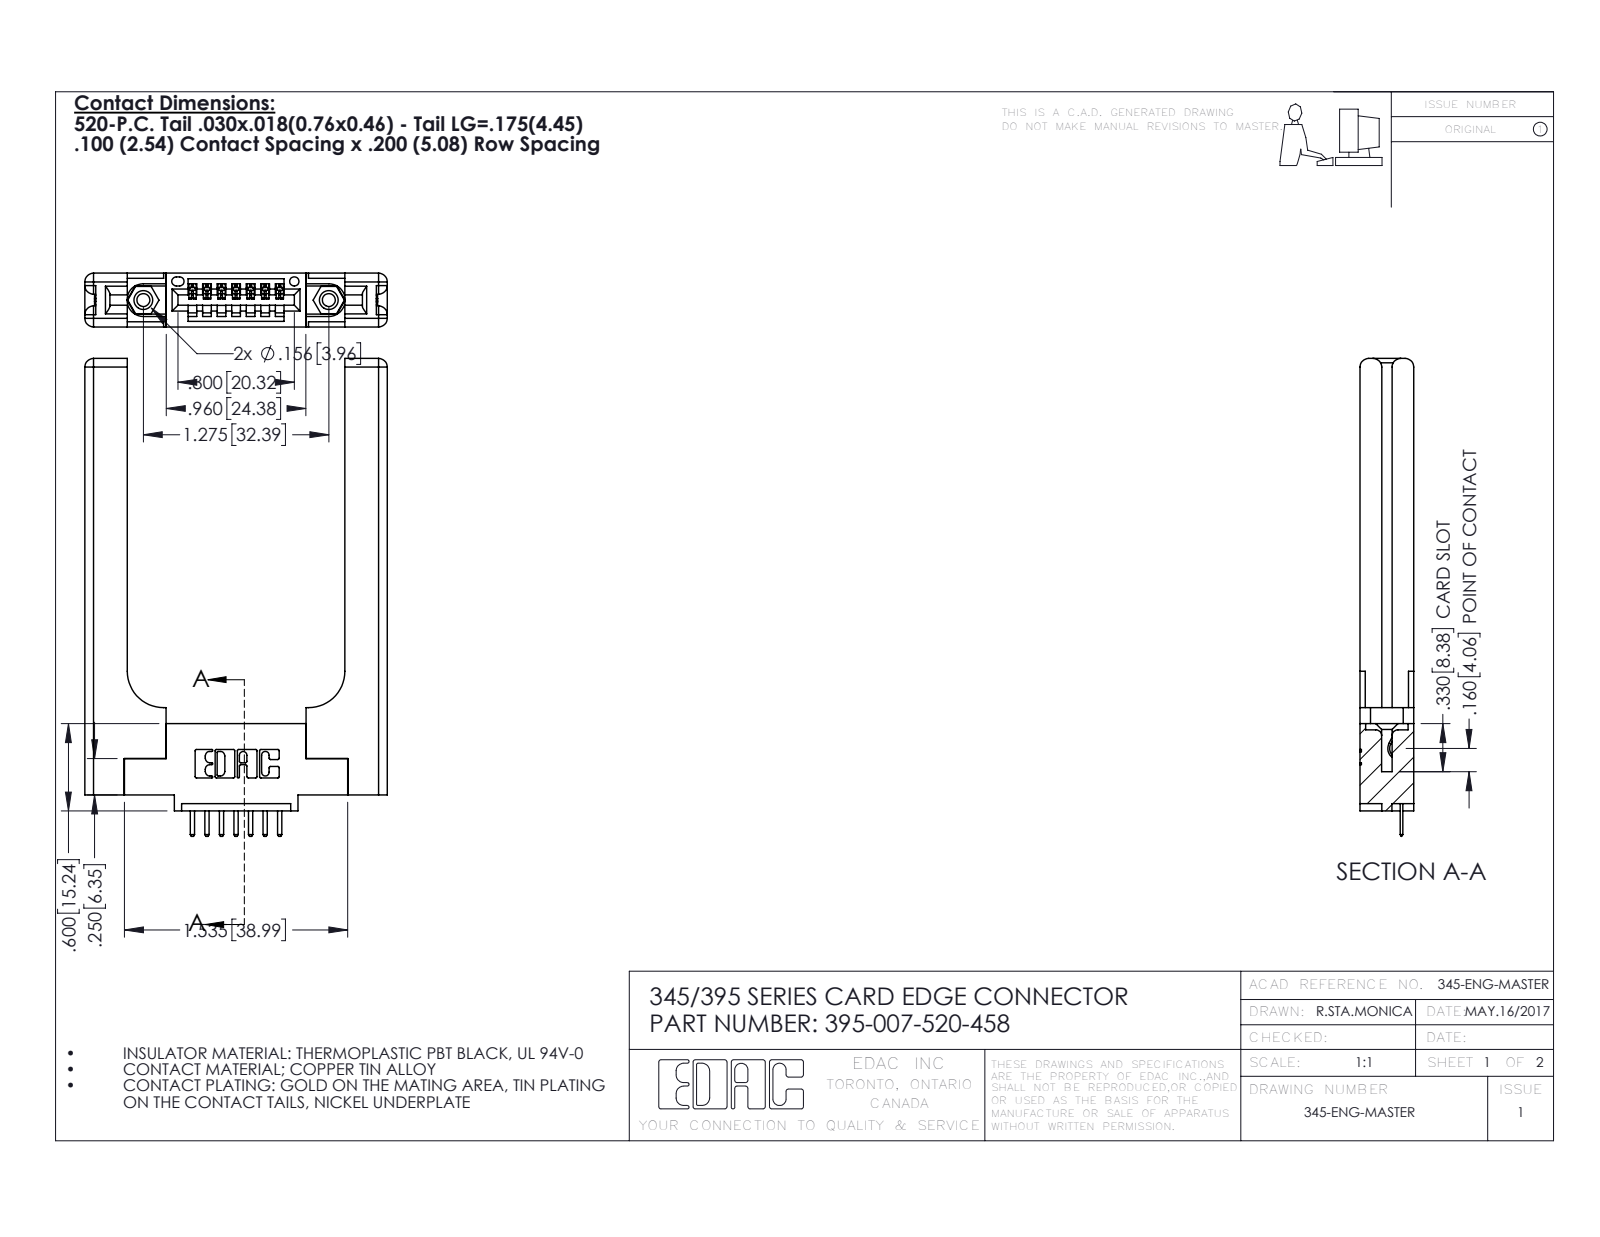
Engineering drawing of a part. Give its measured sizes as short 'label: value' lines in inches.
name: 345-292-001_345-293-120; 345-220-058_345-220-058; 345 Part_0.110 Offset - 0.156 Dia-TH; 395-007-520-458 (+1 more)
written by: SolidWorks 2016 (CONFIG_CONTROL_DESIGN)
unit: in
bodies: 12 solids, 820 faces (526 planar, 234 cylindrical, 60 other)
size: 3.285 × 2.079 × 0.37
volume: 0.802 in³; area: 17.06 in²
holes: 2× ⌀0.089, 2× ⌀0.125, 2× ⌀0.156, 1× ⌀0.064
bosses: 2× ⌀0.155
rounds: 22× R0.01, 16× R0.01, 16× R0.06, 14× R0.006, 6× R0.007, 6× R0.031, 3× R0.026, 2× R0.03
face distances: 0.37, 0.15, 0.22, 0.072, 0.148, 0.077, 1.496, 0.298, 0.071, 0.292
hole spacings: 0.27, 1.045, 1.275
